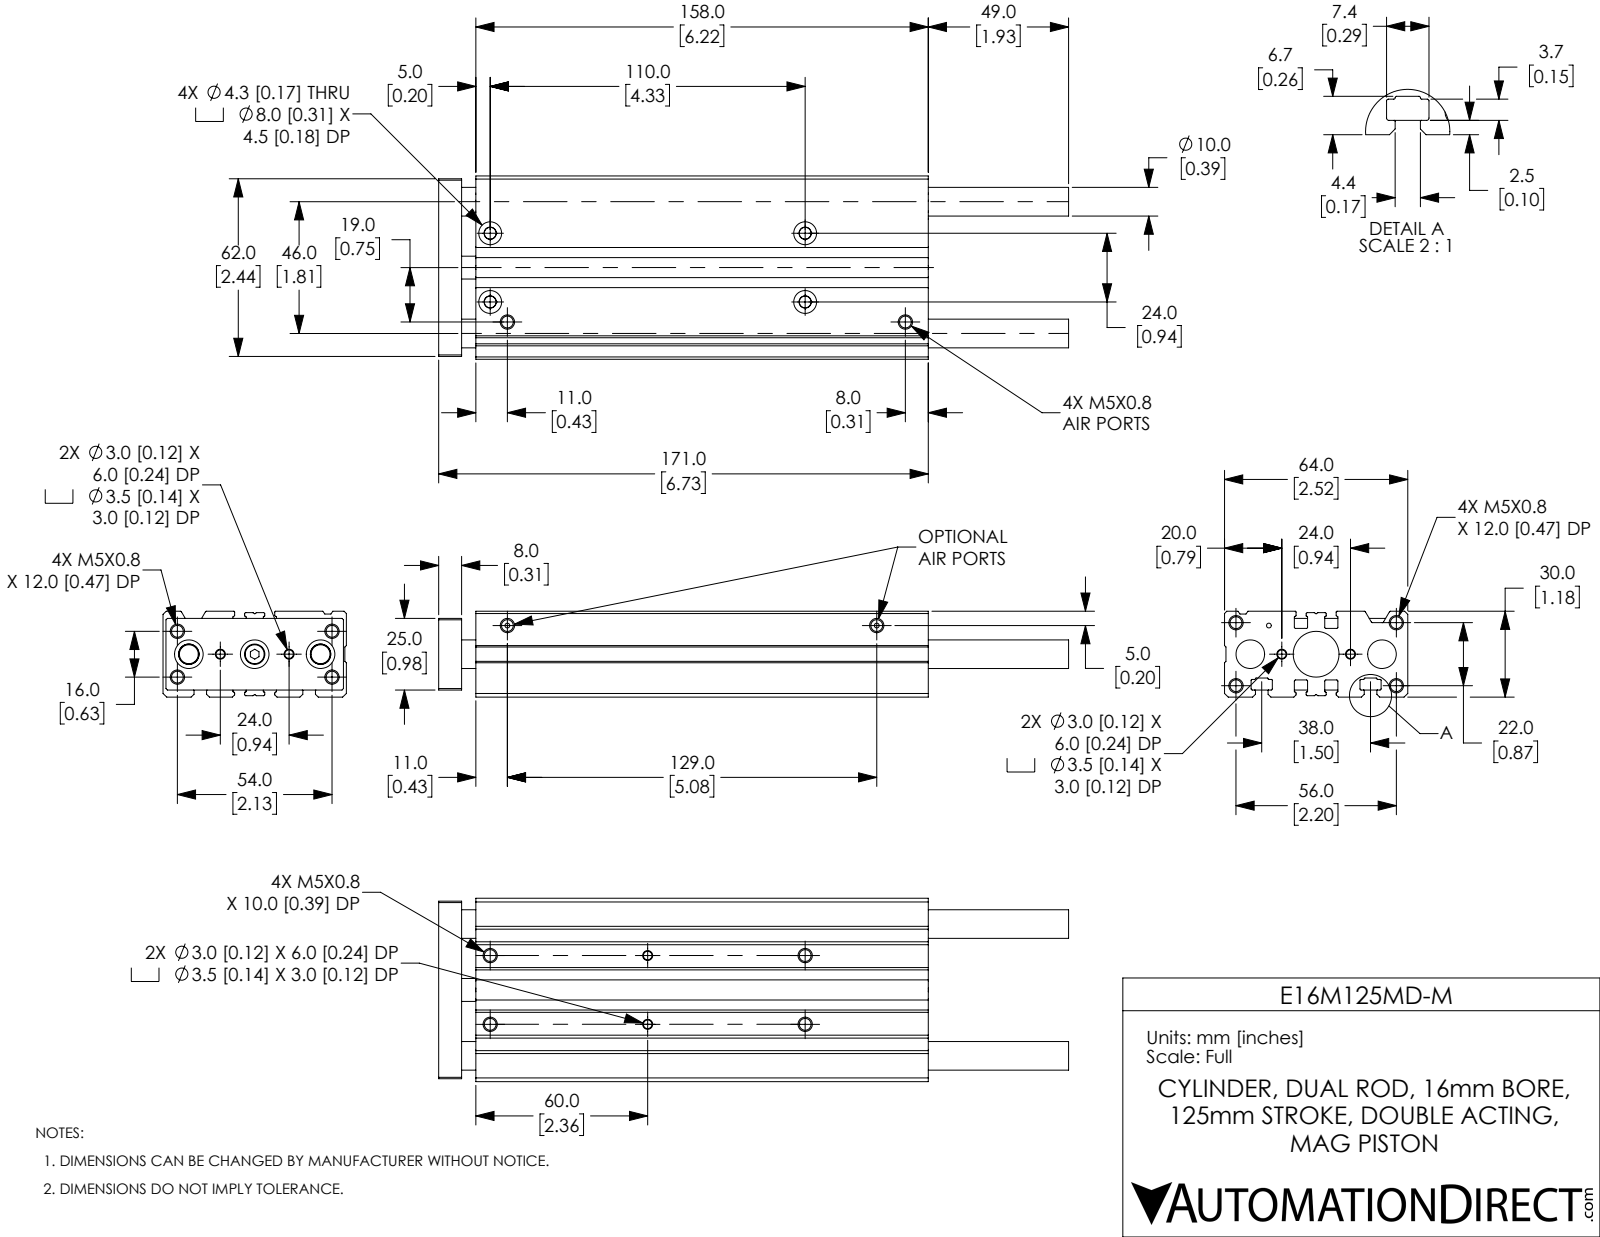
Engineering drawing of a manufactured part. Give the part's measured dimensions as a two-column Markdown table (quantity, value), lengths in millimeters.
| quantity | value |
| --- | --- |
| part name | E16M125MD-M; E16M125MD-M_ENDPLATE; E16M125MD-M_BODY |
| STEP written by | SolidWorks 2019 (CONFIG_CONTROL_DESIGN) |
| units | millimeters |
| bodies | 5 solids, 411 faces (133 planar, 192 cylindrical, 86 other) |
| overall size | 220 × 64 × 30 |
| volume | 264 869 mm³ |
| surface area | 92 219 mm² |
| round holes (diameter × count) | 4.13 × 16, 3 × 4, 3.5 × 4, 4.3 × 4, 8 × 4, 1.67 × 3, 5 × 3, 10 × 3, 7.11 × 2, 10 × 1, 16 × 1, 16 × 1 |
| round bosses / shafts (diameter × count) | 8 × 1, 7.11 × 1 |
| partial cylindrical surfaces (radius × count) | 0.2 × 22, 0.4 × 20, 0.25 × 8, 0.3 × 6, 0.5 × 4 |
| main face-to-face distances | 30, 0.5, 6, 64, 29, 24.4, 3.5, 24, 35, 39.6 |
| hole center spacings | 3.16, 8.94, 12.08, 17, 19.03, 19.42, 24, 28.16 |
